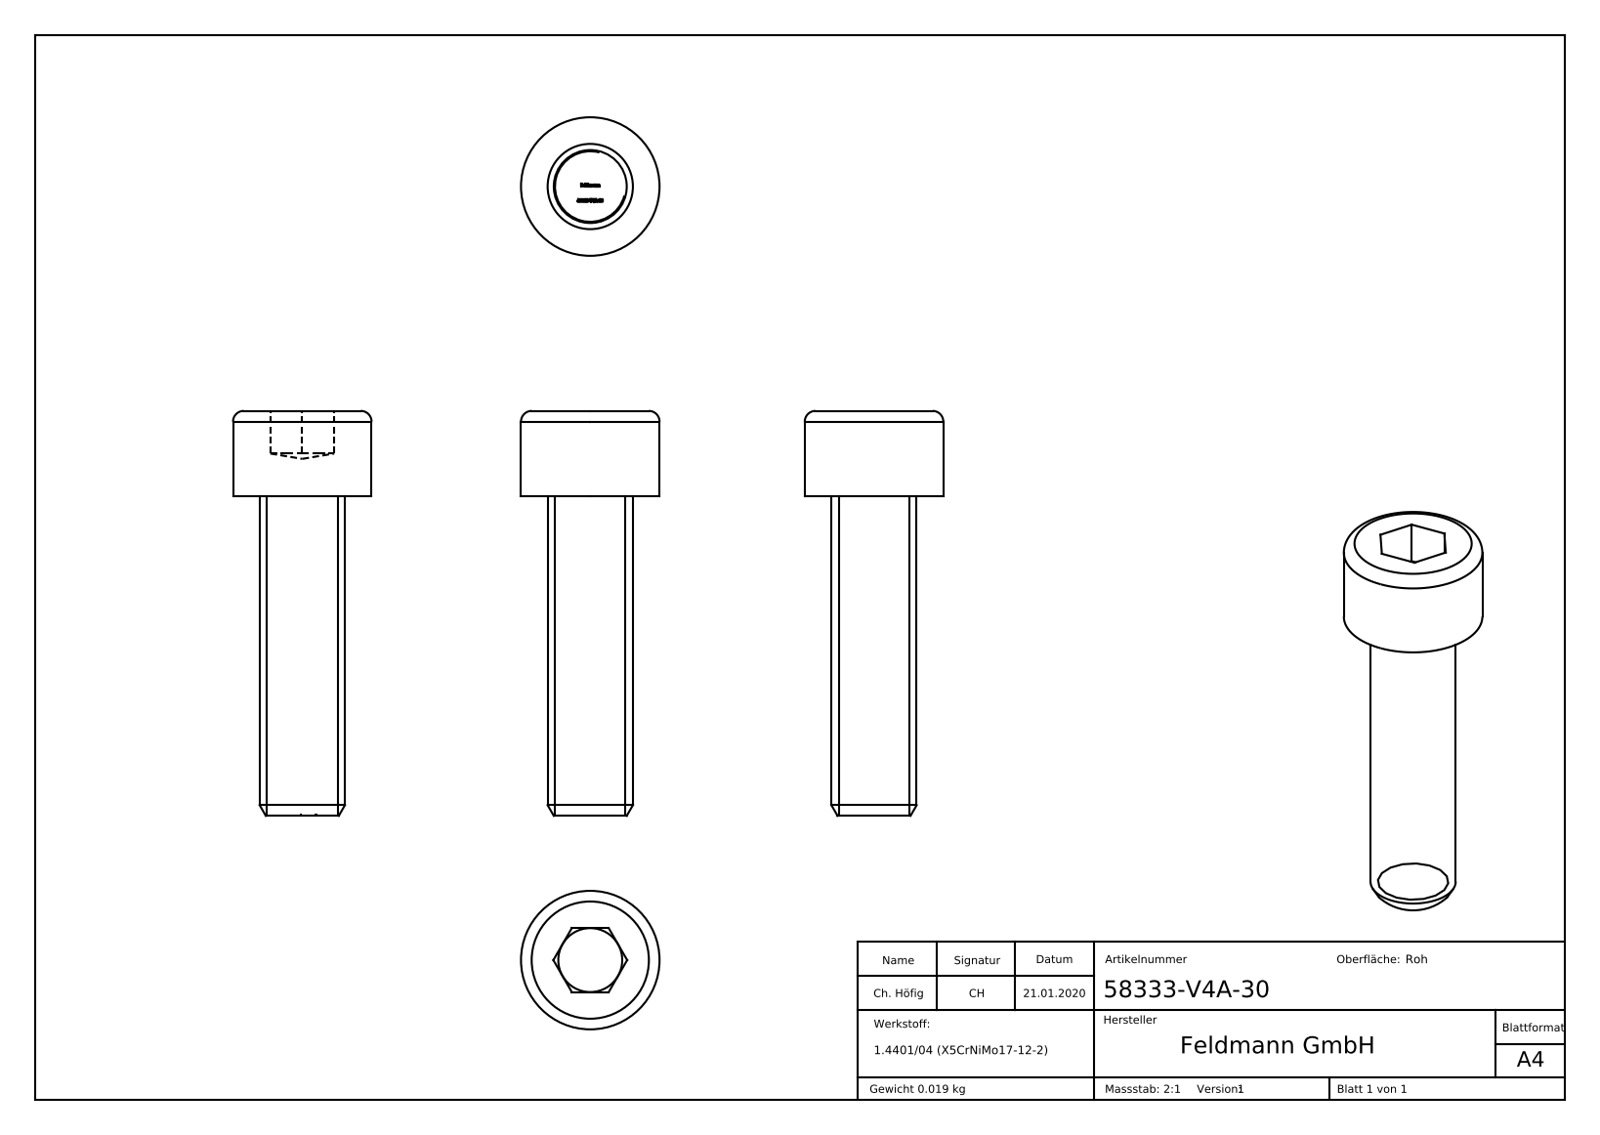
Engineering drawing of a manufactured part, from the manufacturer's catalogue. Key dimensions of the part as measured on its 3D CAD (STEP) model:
Part name (STEP PRODUCT): 58333-V4A-30
STEP written by: SolidWorks 2015 (CONFIG_CONTROL_DESIGN)
Units: millimetres
Bodies: 1 solid, 297 faces (154 planar, 2 cylindrical, 141 other)
Overall size (bounding box): 39 × 13 × 13
Volume: 2 425 mm³ · Surface area: 1 402 mm²
Round bosses / shafts (diameter × count): ⌀13 ×1, ⌀8 ×1
Main face-to-face distances: 8, 6, 30, 38, 4, 34, 29.9, 33.9, 37.9, 1.33
